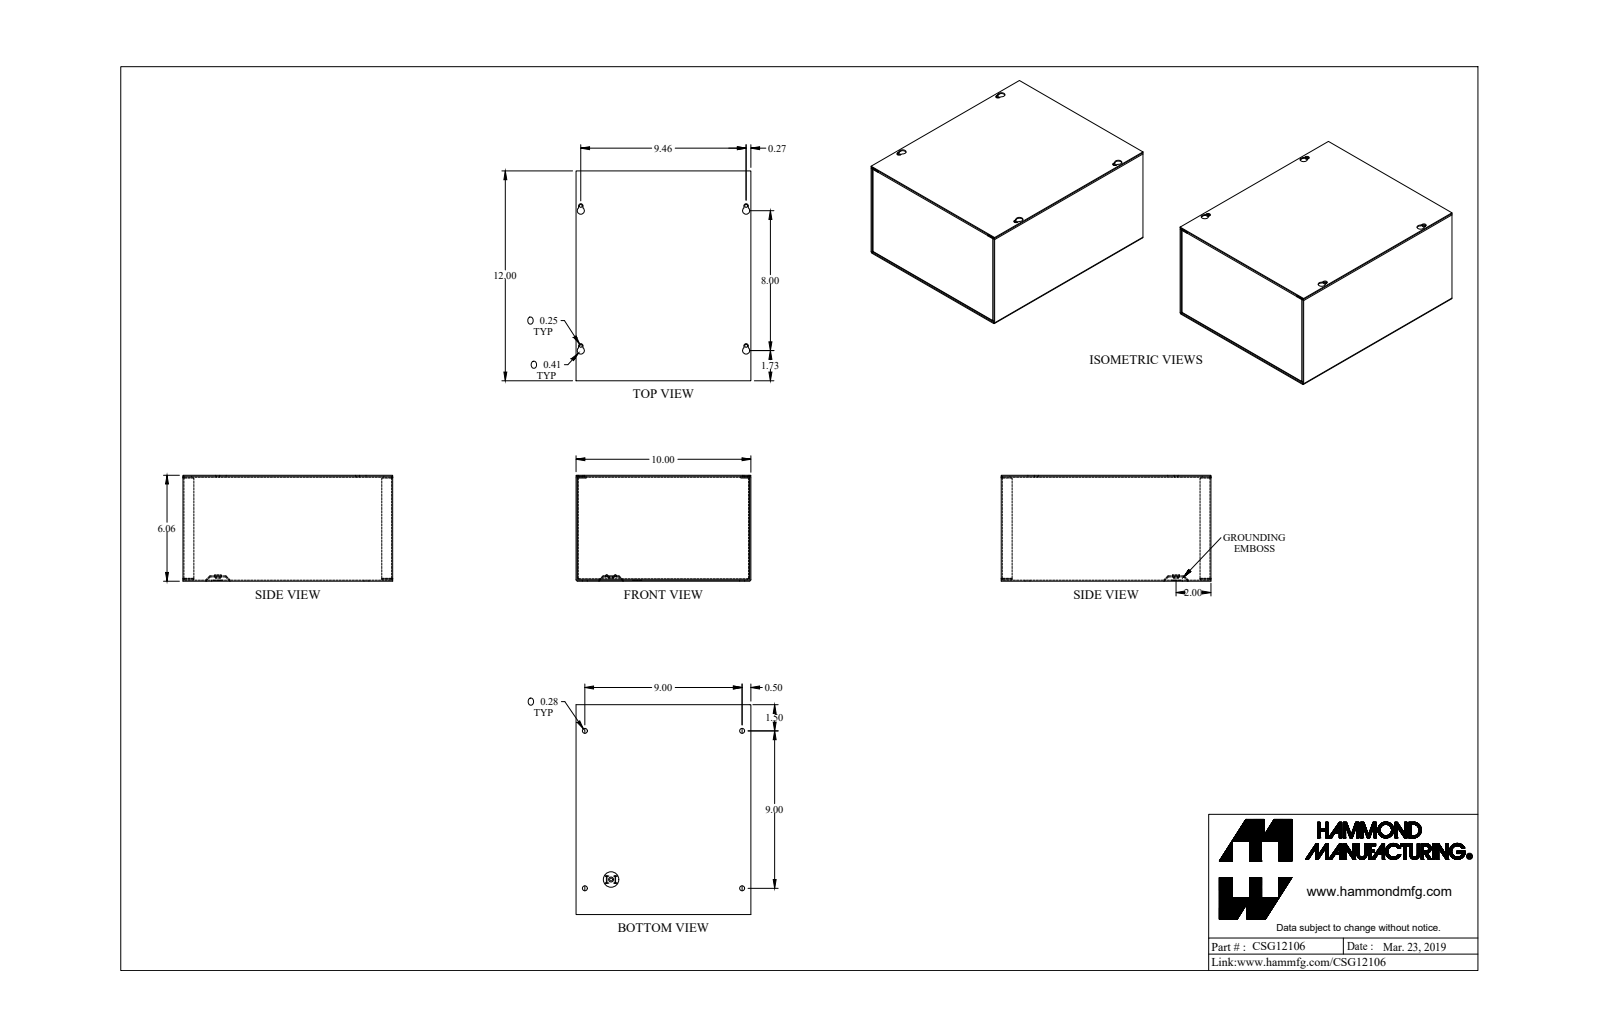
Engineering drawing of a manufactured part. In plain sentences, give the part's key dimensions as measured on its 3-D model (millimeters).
The part is named "CSG12106_Default". Its 3-D file was written by "SolidWorks 2019 (CONFIG_CONTROL_DESIGN)". It is 4 solids with 205 faces: 125 planar, 72 cylindrical and 8 other. Overall it measures 304.8 by 254 by 153.8 millimeters. Its volume is 502 900 cubic millimeters and its surface area 701 900 square millimeters. Round holes: 5 of diameter 4.3, 4 of diameter 7.1, 1 of diameter 12.7. Round bosses or shafts: 1 of diameter 12.5, 1 of diameter 7.2. Partial cylindrical surfaces (rounded edges, fillets, slot ends): 12 of radius 0.7, 12 of radius 2.2, 8 of radius 1.4, 4 of radius 3.2, 4 of radius 5.2. The main face-to-face distances are 1.4, 152.4, 252.6, 151, 153.8, 303.4, 254, 251.1, 304.8, 301.9. The hole center spacings are 14, 216, 228.6, 234.8, 318.7, 203.2, 240.3, 314.7.
